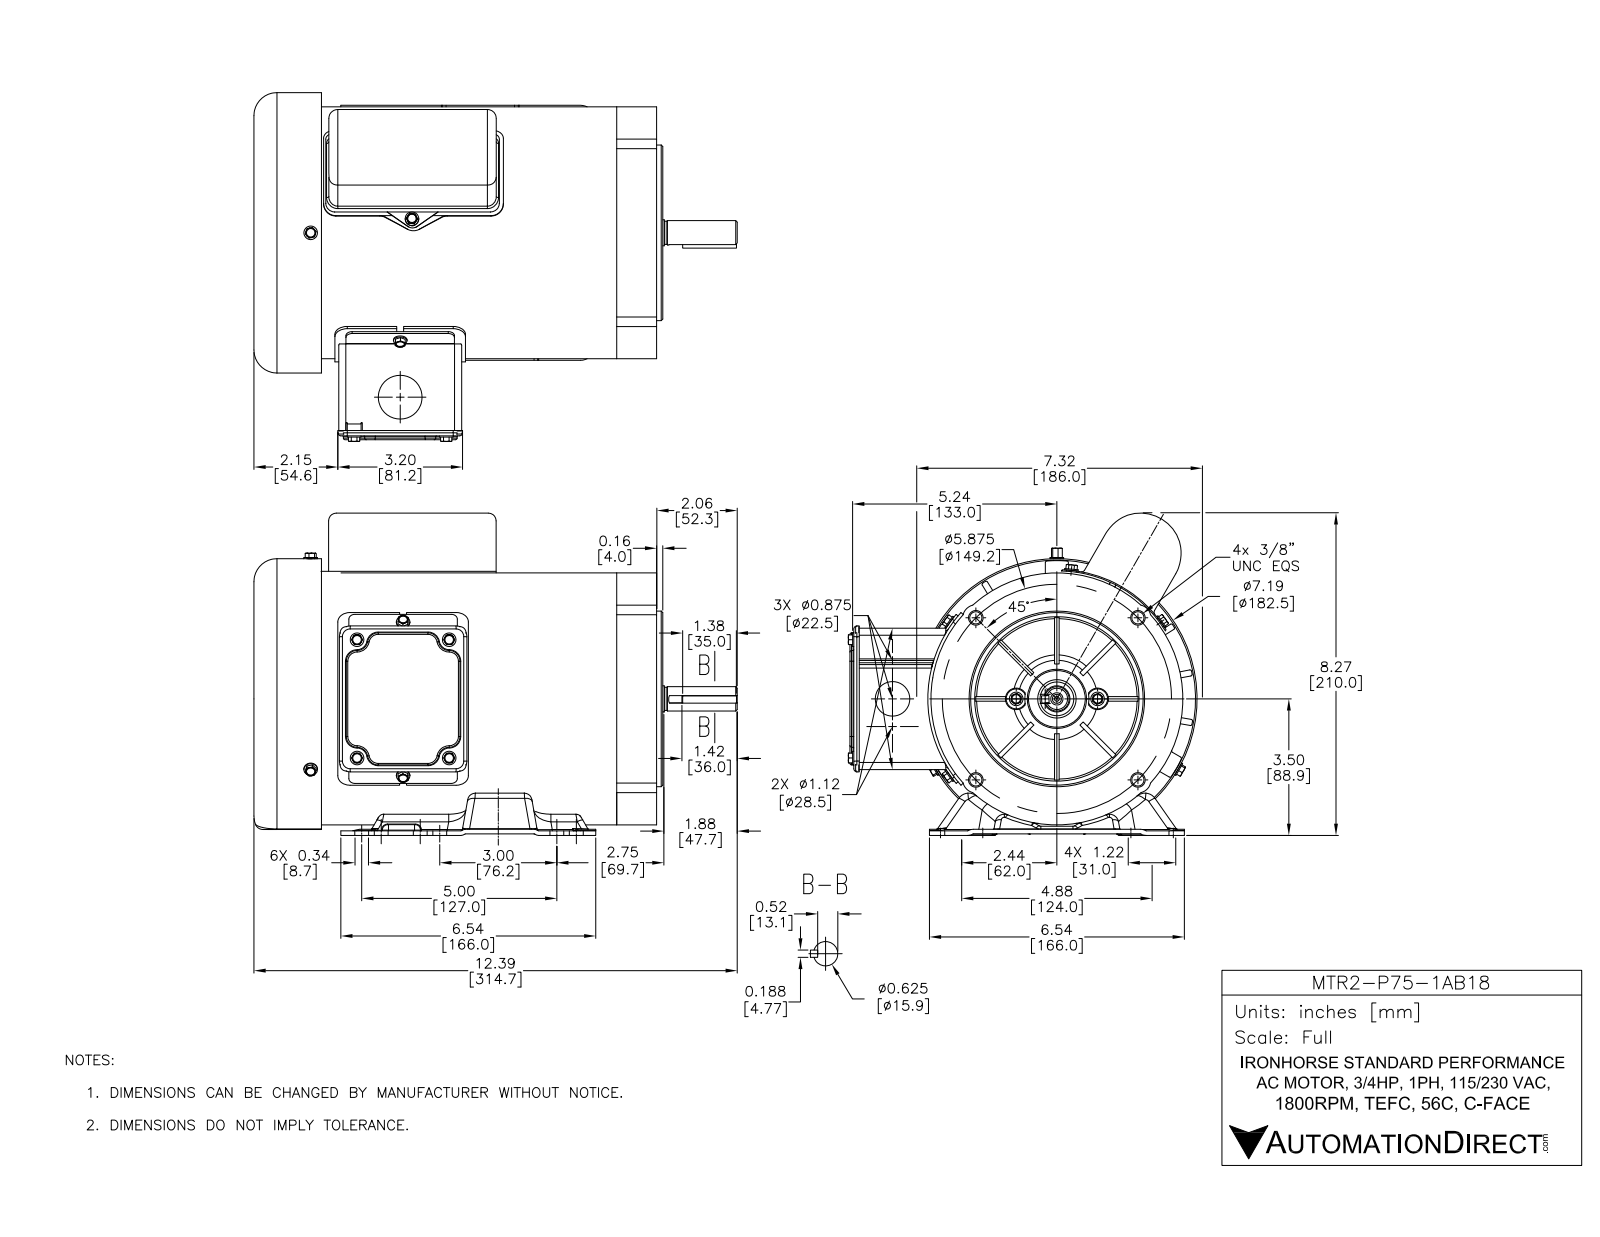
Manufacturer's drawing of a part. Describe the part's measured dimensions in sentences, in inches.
The part is named "MTR2-P75-1AB18". Its 3-D file was written by "SolidWorks 2016 (AUTOMOTIVE_DESIGN)". It is 53 solids with 3179 faces: 951 planar, 1052 cylindrical and 1176 other. Overall it measures 12.146 by 8.938 by 8.3 inches. Its volume is 47.67 cubic inches and its surface area 1 087 square inches. Round holes: 12 of diameter 0.197, 11 of diameter 0.219, 10 of diameter 0.118, 8 of diameter 0.276, 6 of diameter 0.217, 6 of diameter 0.344, 5 of diameter 0.136, 4 of diameter 0.059, 4 of diameter 0.15, 4 of diameter 0.177, 4 of diameter 0.313, 3 of diameter 0.157. Round bosses or shafts: 11 of diameter 0.164, 6 of diameter 0.348, 6 of diameter 0.25, 5 of diameter 0.348, 4 of diameter 0.276, 2 of diameter 0.414, 2 of diameter 0.19, 2 of diameter 0.098. Partial cylindrical surfaces (rounded edges, fillets, slot ends): 125 of radius 0.118, 38 of radius 0.02, 38 of radius 0.039, 32 of radius 0.157, 26 of radius 0.138, 20 of radius 0.228, 19 of radius 0.276, 17 of radius 0.197. The main face-to-face distances are 0.118, 0.039, 0.063, 8.898, 1.024, 1.142, 10.079, 10.039, 0.098, 0.047. The hole center spacings are 4.221, 2.008, 3.031, 0.094, 2.32, 2.409, 2.834, 2.937.
